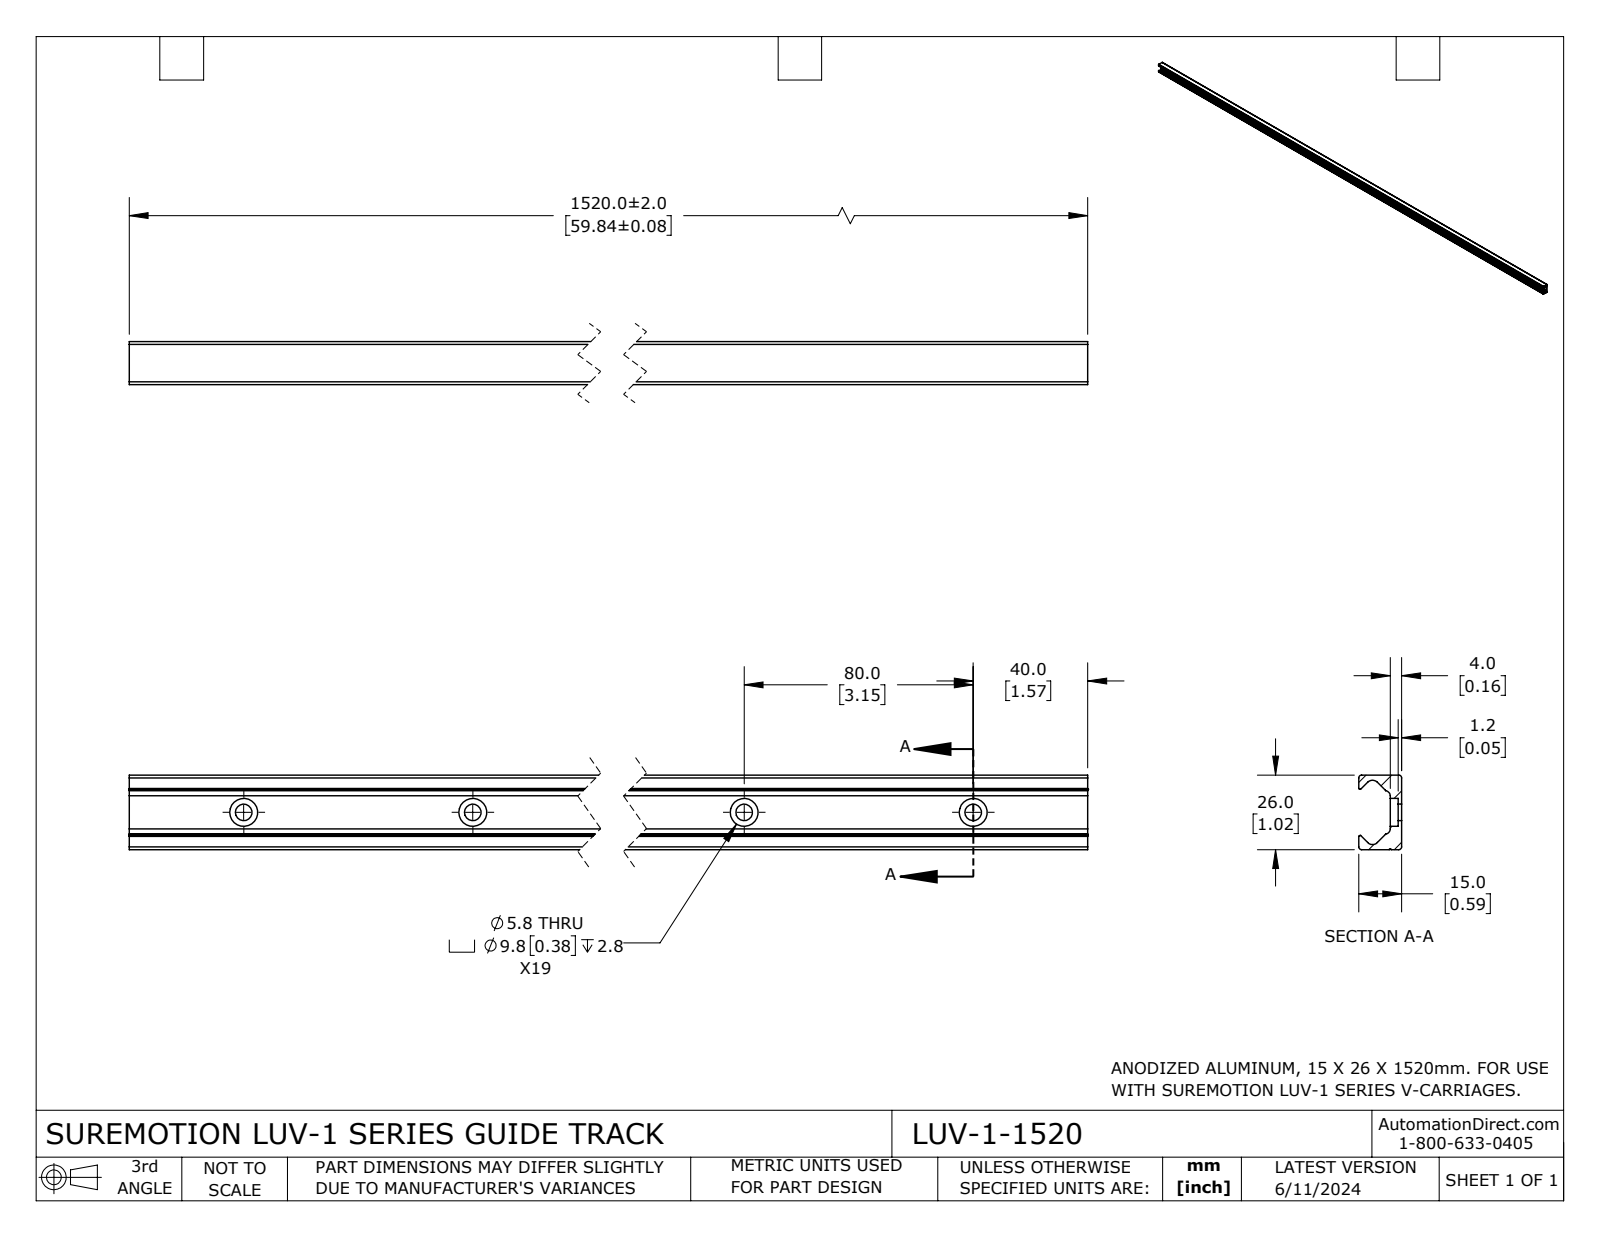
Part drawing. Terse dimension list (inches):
name: LUV-1-1520
written by: SolidWorks 2023 (CONFIG_CONTROL_DESIGN)
unit: in
bodies: 1 solid, 123 faces (32 planar, 91 cylindrical, 0 other)
size: 59.843 × 1.024 × 0.591
volume: 16.7 in³; area: 249.8 in²
holes: 19× ⌀0.228, 19× ⌀0.384
rounds: 4× R0.039, 2× R0.02, 2× R0.025, 2× R0.03, 2× R0.07, 2× R0.094, 1× R0.013
face distances: 1.024, 0.158, 0.591, 0.433, 0.68, 0.048, 0.11, 0.544, 59.843
hole spacings: 3.15, 6.299, 9.449, 12.598, 15.748, 18.898, 22.047, 25.197
